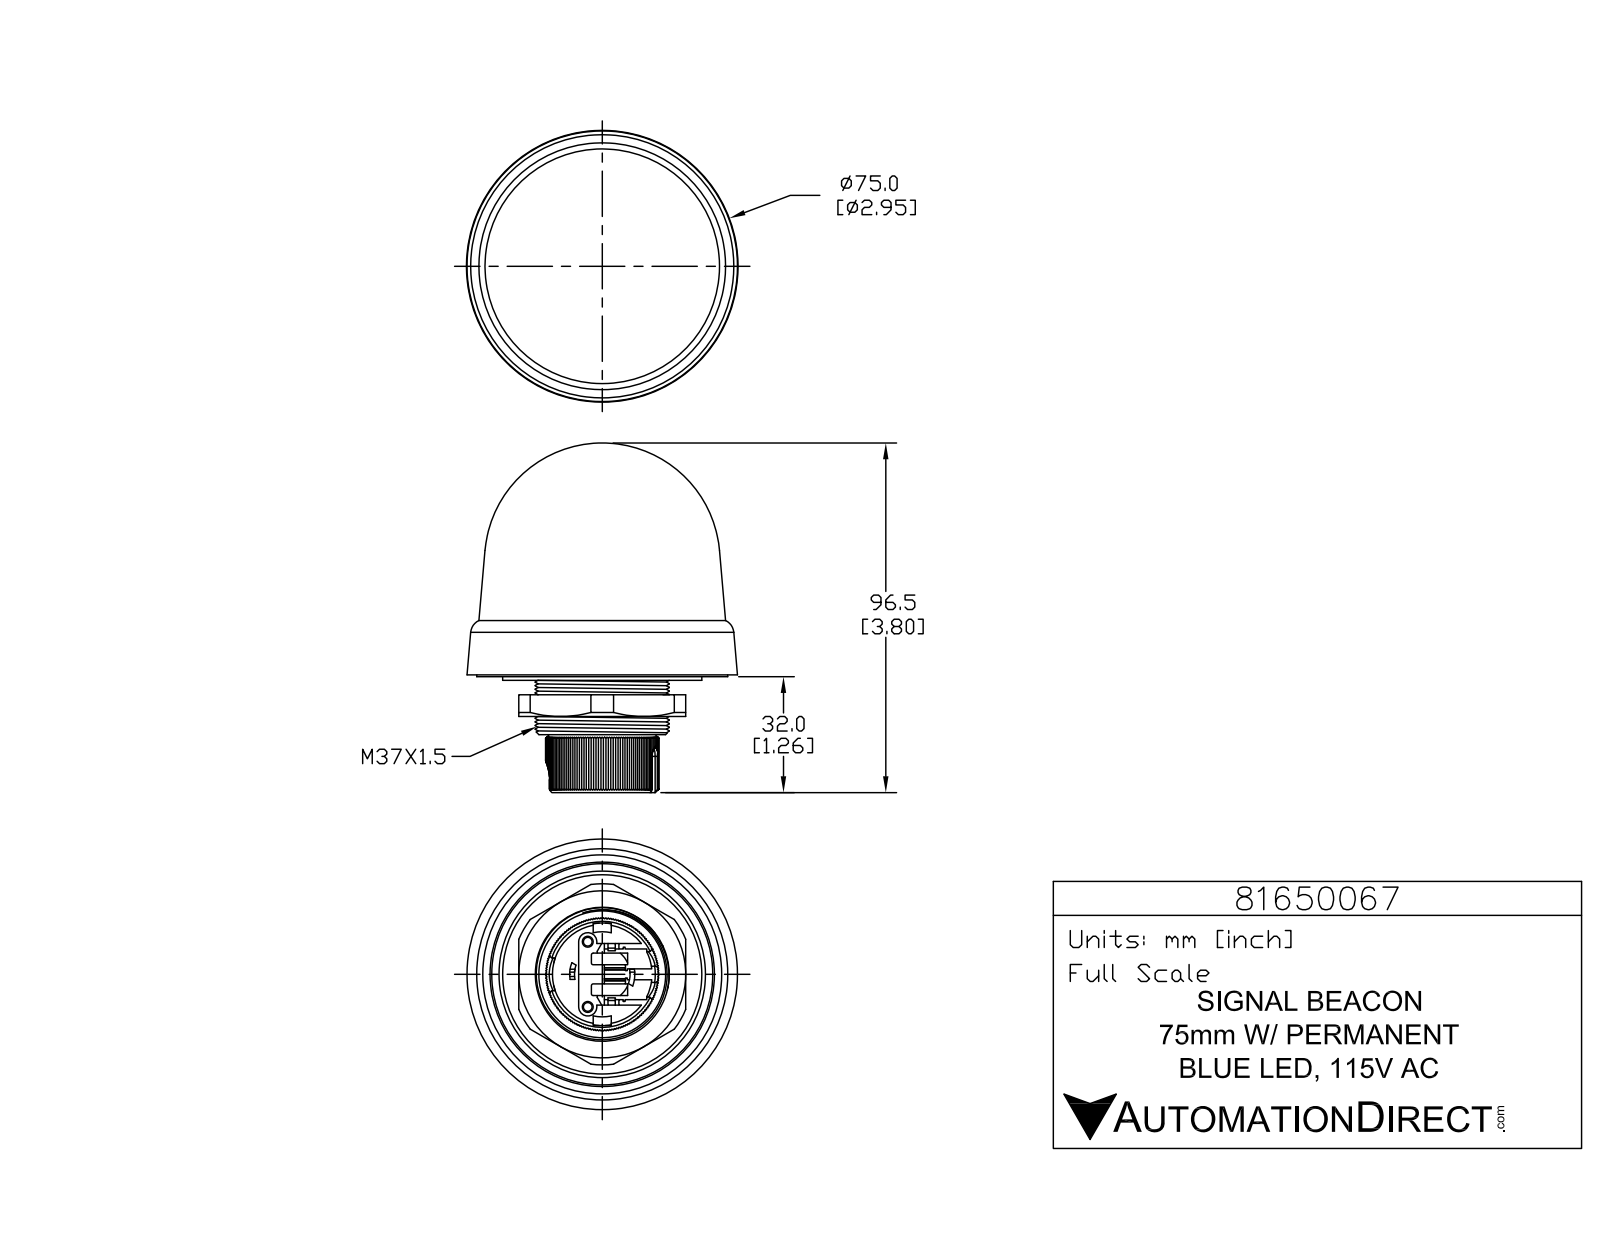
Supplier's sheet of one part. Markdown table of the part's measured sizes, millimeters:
| quantity | value |
| --- | --- |
| part name | 81650067 |
| STEP written by | SolidWorks 2019 (CONFIG_CONTROL_DESIGN) |
| units | millimeters |
| bodies | 3 solids, 560 faces (432 planar, 80 cylindrical, 48 other) |
| overall size | 96.5 × 74.7 × 74.7 |
| volume | 202 500 mm³ |
| surface area | 37 860 mm² |
| round holes (diameter × count) | 2.4 × 2, 3 × 2, 15.3 × 1, 29 × 1 |
| round bosses / shafts (diameter × count) | 5.5 × 2, 1.7 × 2, 55 × 1, 37 × 1, 23.5 × 1 |
| partial cylindrical surfaces (radius × count) | 0.2 × 6, 1 × 6, 0.5 × 4, 0.8 × 2, 2 × 2, 2.5 × 2, 4.5 × 1, 9 × 1 |
| main face-to-face distances | 4.5, 9, 5, 11, 13, 8.5, 1.5, 10, 3, 4 |
| hole center spacings | 9.9, 18 |
